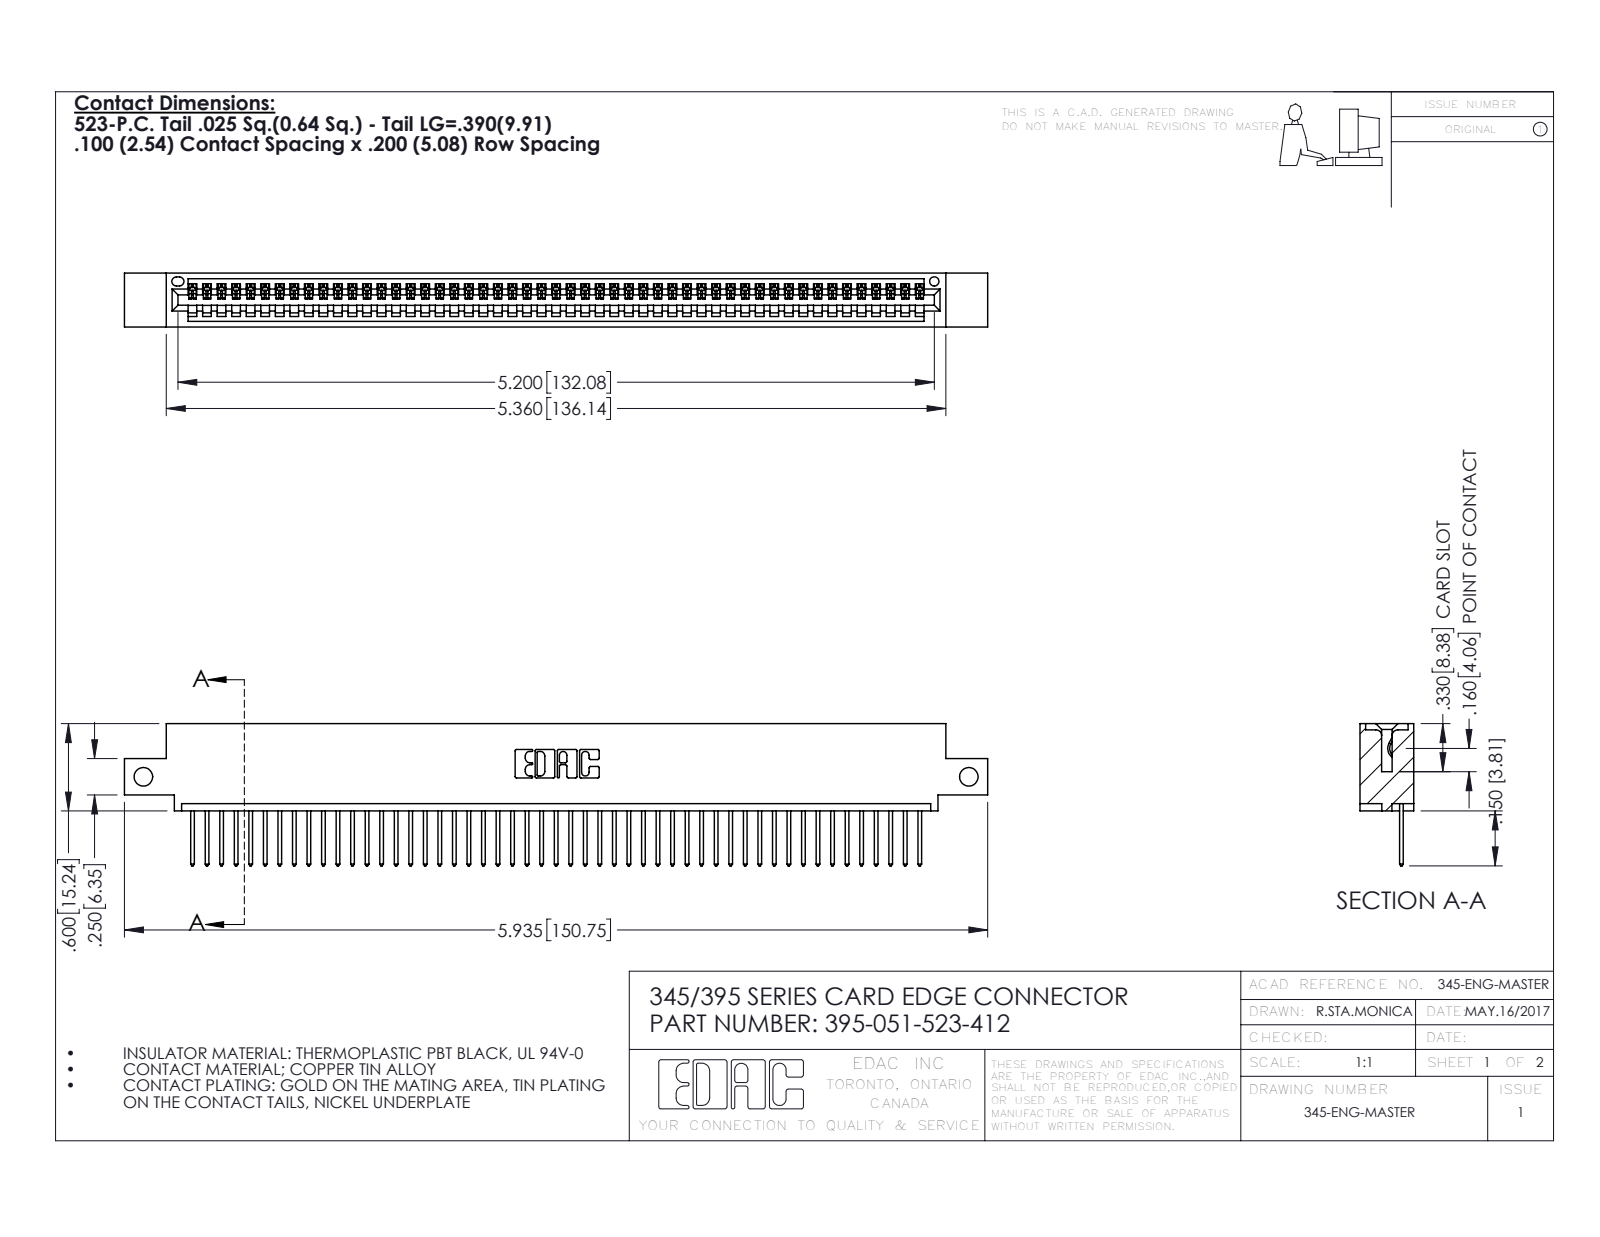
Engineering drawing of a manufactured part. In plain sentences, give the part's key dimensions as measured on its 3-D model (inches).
The part is named "345-292-001_345-293-123; 345 Part_0.110 Offset - Side Mount; 395-051-523-412". Its 3-D file was written by "SolidWorks 2016 (CONFIG_CONTROL_DESIGN)". It is 52 solids with 3088 faces: 2124 planar, 964 cylindrical and 0 other. Overall it measures 5.935 by 0.977 by 0.37 inches. Its volume is 0.867 cubic inches and its surface area 29.46 square inches. Round holes: 2 of diameter 0.128, 1 of diameter 0.064. Partial cylindrical surfaces (rounded edges, fillets, slot ends): 102 of radius 0.006, 102 of radius 0.01, 22 of radius 0.01, 6 of radius 0.007, 6 of radius 0.031, 3 of radius 0.026, 2 of radius 0.031, 2 of radius 0.04. The main face-to-face distances are 0.298, 0.072, 0.37, 0.098, 0.272, 0.025, 0.2, 0.225, 0.149, 0.072. The hole center spacings are 5.675.
